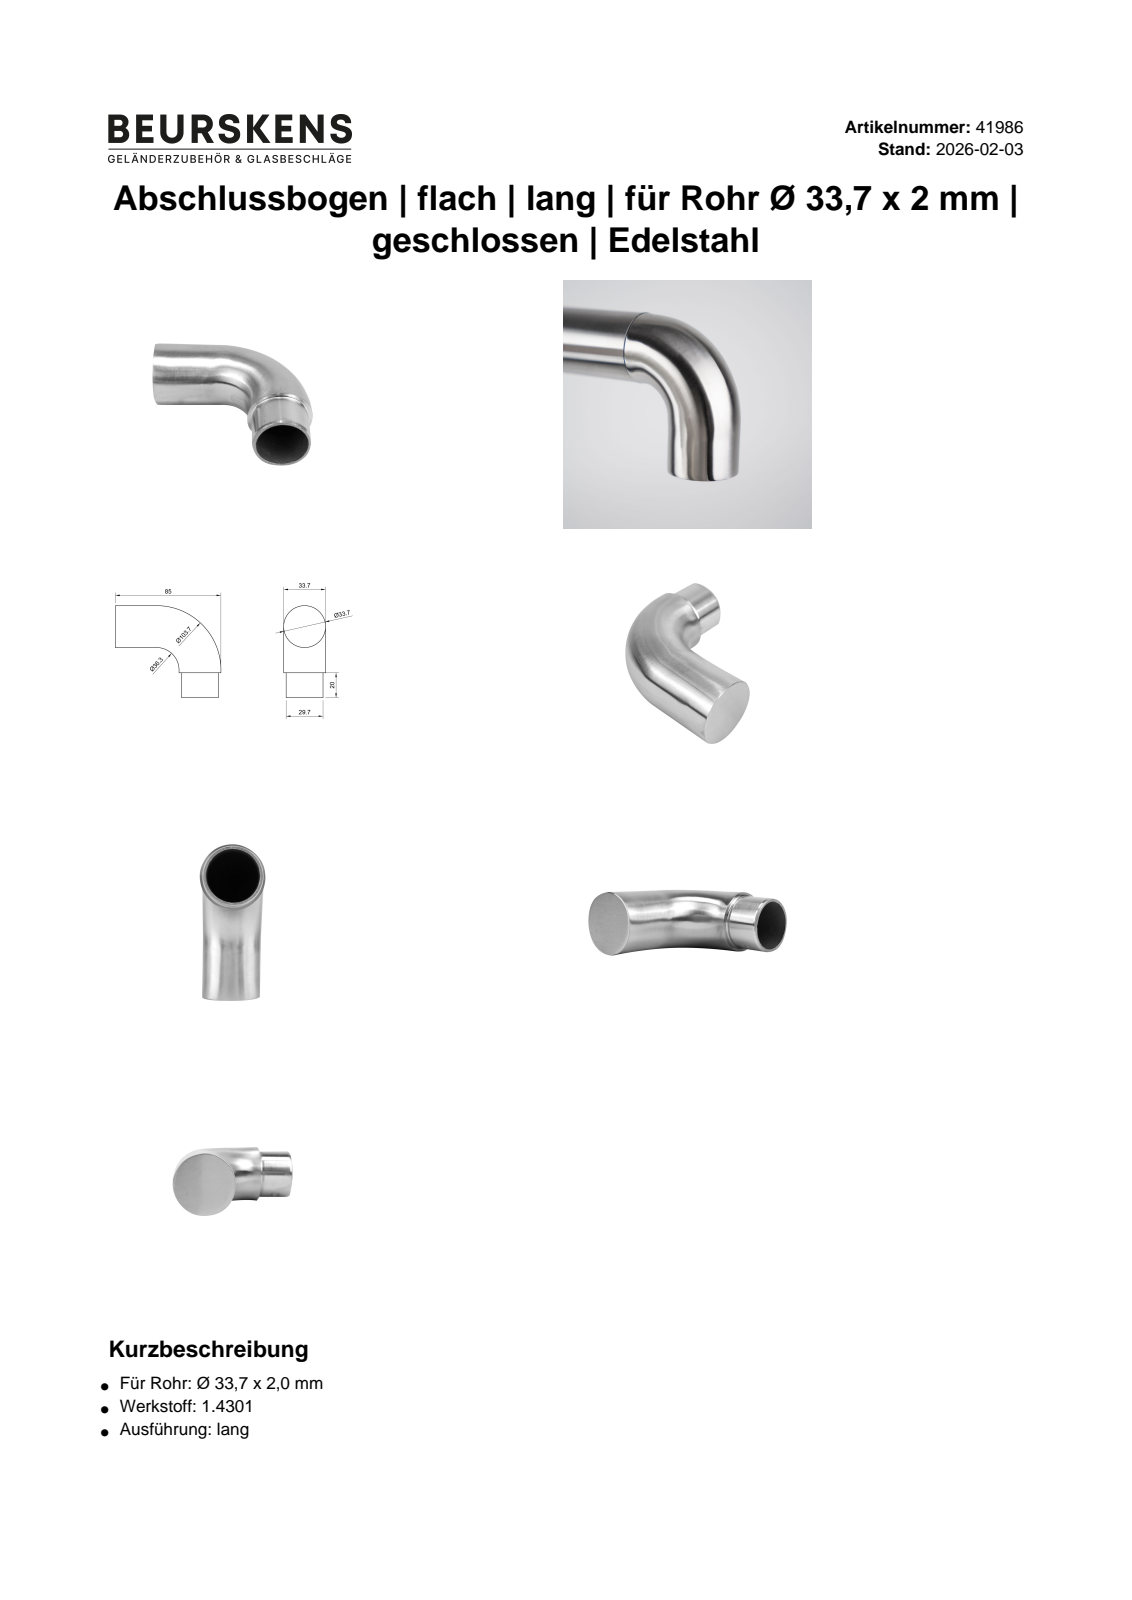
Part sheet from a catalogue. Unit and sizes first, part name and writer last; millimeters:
Units: millimetres
Overall size (bounding box): 85 × 74 × 33.7
Round holes (diameter × count): ⌀29.7 ×2, ⌀25.7 ×1
Round bosses / shafts (diameter × count): ⌀33.7 ×2
Main face-to-face distances: 2, 20, 22
Volume: 23 196 mm³ · Surface area: 23 382 mm²
Bodies: 1 solid, 13 faces (5 planar, 6 cylindrical, 2 other)
Part name (STEP PRODUCT): 41986
STEP written by: Autodesk Inventor 2022 (AUTOMOTIVE_DESIGN)
